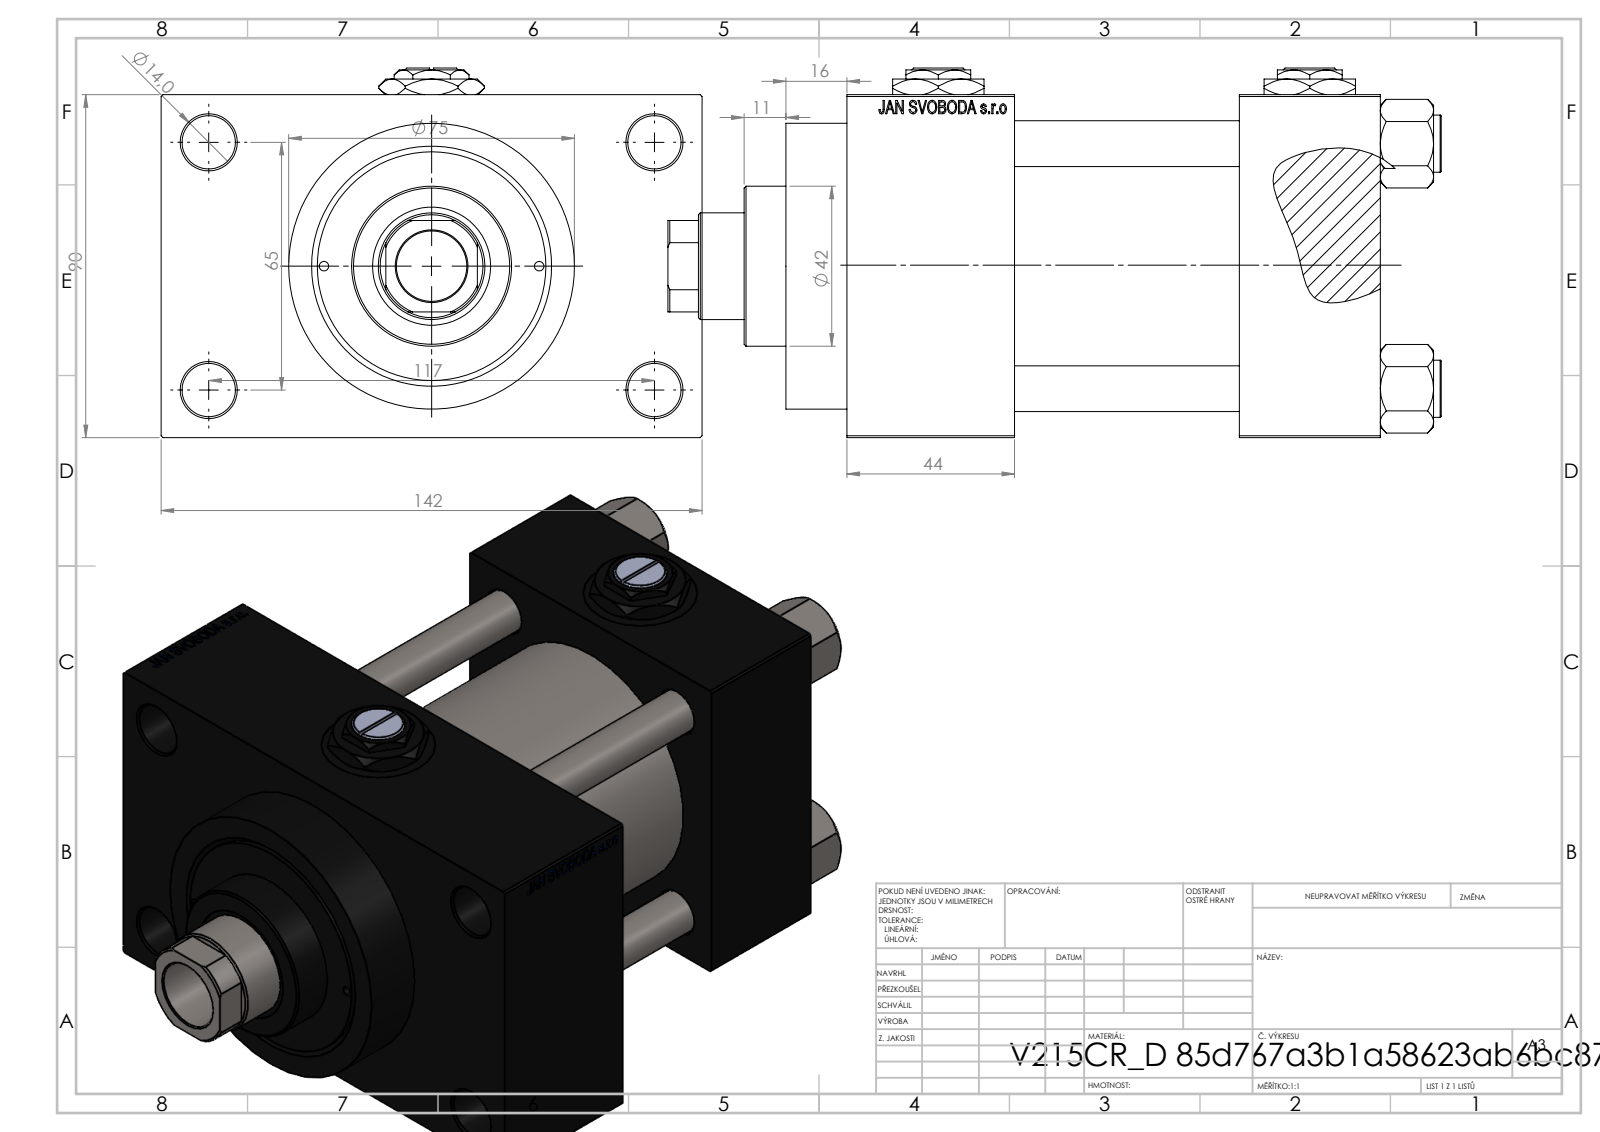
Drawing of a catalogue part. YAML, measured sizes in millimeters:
part_name: "V215CR_VCP_D; NUT_M5_D; V215CR_D_TYCINKA; V215CR_D_Body (+2 more)"
step_written_by: "SolidWorks 2019 (CONFIG_CONTROL_DESIGN)"
units: millimeters
bodies: {solids: 13, faces: 1213, planar: 547, cylindrical: 104, other: 562}
overall_size: [203, 142, 97]
volume: 1099000
surface_area: 203152
round_holes:
  - {diameter: 12, count: 4}
  - {diameter: 14, count: 4}
  - {diameter: 2.5, count: 2}
  - {diameter: 7, count: 2}
  - {diameter: 20.96, count: 2}
  - {diameter: 30, count: 2}
  - {diameter: 18.5, count: 1}
  - {diameter: 28, count: 1}
  - {diameter: 31, count: 1}
  - {diameter: 50, count: 1}
  - {diameter: 60, count: 1}
  - {diameter: 63, count: 1}
round_bosses_or_shafts:
  - {diameter: 15, count: 4}
  - {diameter: 75, count: 1}
  - {diameter: 69, count: 1}
  - {diameter: 42, count: 1}
partial_cylinders:
  - {radius: 13.5, count: 1}
face_to_face_distances: [90, 59, 37, 96, 140, 103, 44, 26, 116, 142]
hole_center_spacings: [26.35, 32.39, 44.4, 45.47, 64.3, 66.92, 68.42, 69.81]
